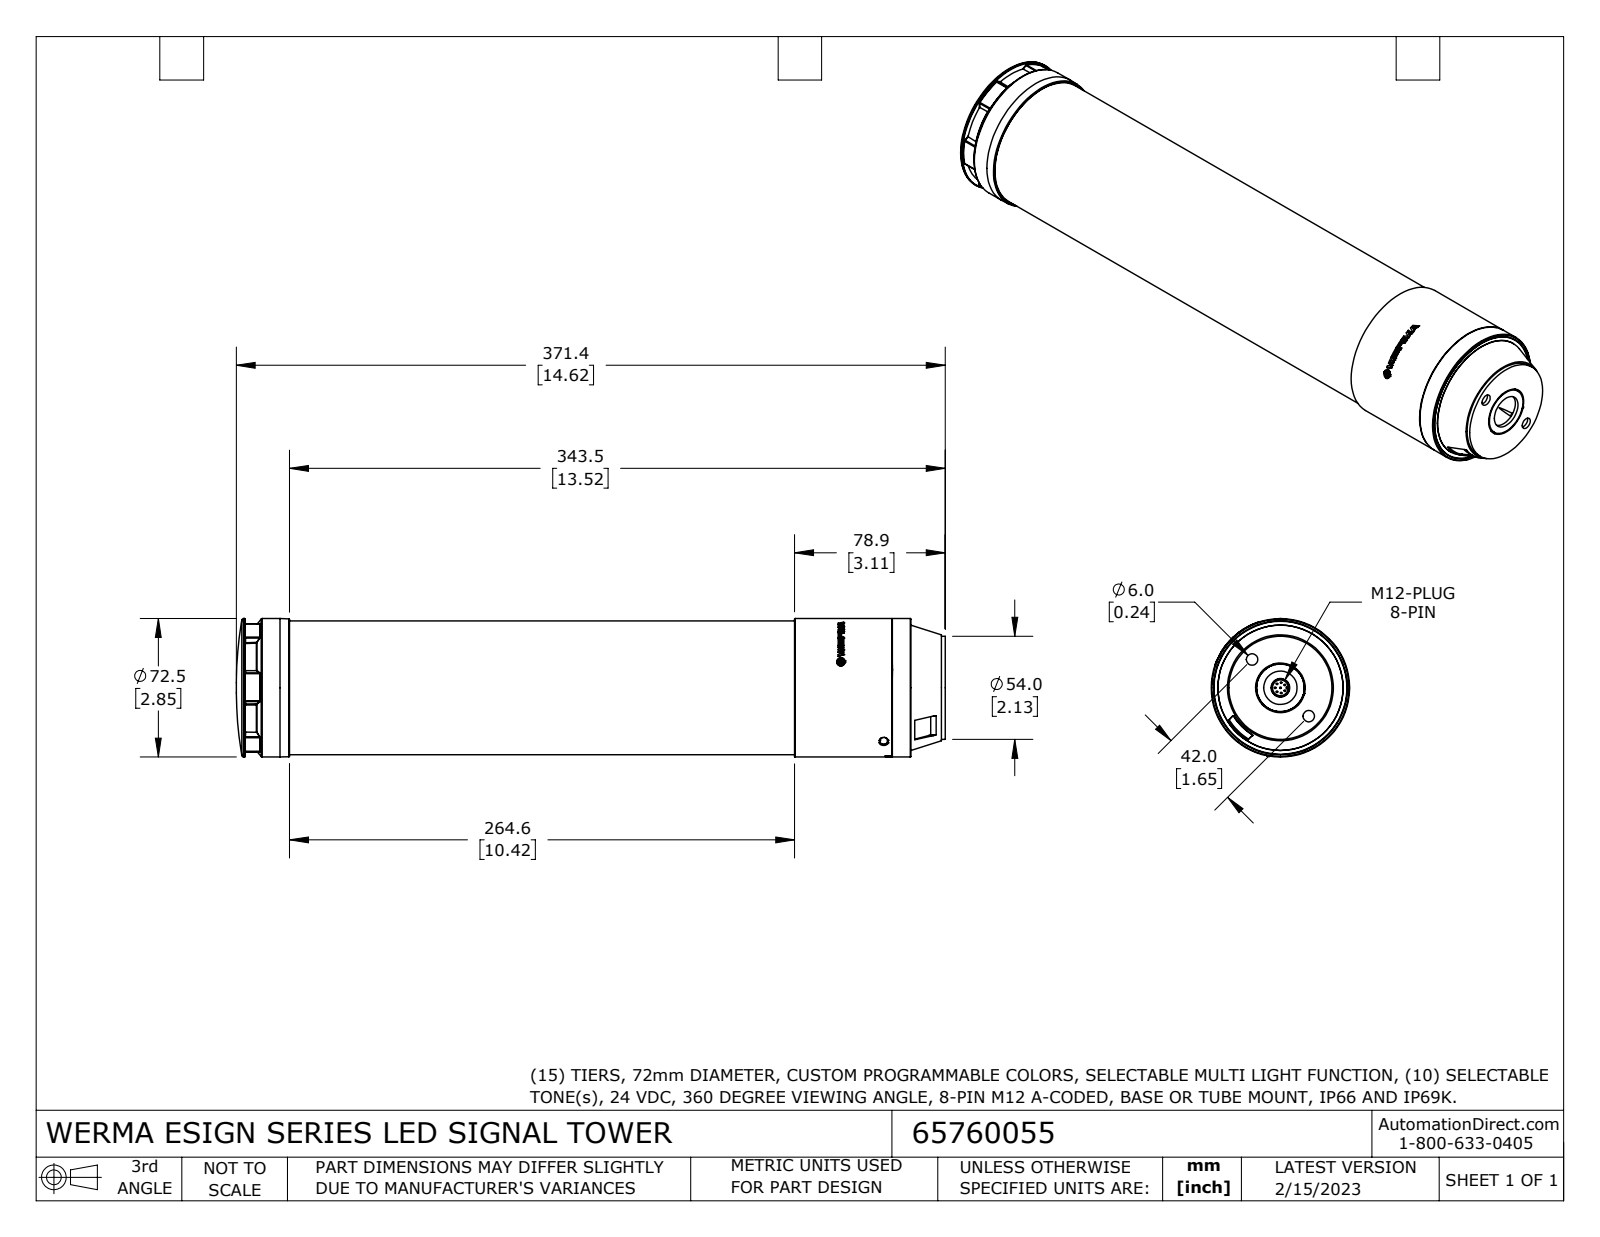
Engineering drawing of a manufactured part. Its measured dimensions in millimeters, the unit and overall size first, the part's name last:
Units: millimetres
Overall size (bounding box): 371.4 × 72.5 × 72.5
Round holes (diameter × count): ⌀6 ×2, ⌀8.3 ×1, ⌀9.7 ×1, ⌀17.5 ×1, ⌀26 ×1
Round bosses / shafts (diameter × count): ⌀0.8 ×8, ⌀72.5 ×1, ⌀70 ×1, ⌀54 ×1, ⌀24.9 ×1, ⌀4.4 ×1
Partial cylindrical surfaces — rounded edges, fillets, slot ends (radius × count): R0.3 ×12, R0.7 ×12, R2 ×2, R2 ×2, R2.5 ×2, R0.2 ×1, R0.3 ×1, R0.4 ×1
Main face-to-face distances: 360.9, 2, 358.9, 24.9, 22.9, 336, 18.1, 16.1, 6.8, 342.7
Hole centre spacings: 21, 42
Volume: 1 388 000 mm³ · Surface area: 100 600 mm²
Bodies: 1 solid, 409 faces (133 planar, 126 cylindrical, 150 other)
Part name (STEP PRODUCT): 65760055
STEP written by: SolidWorks 2021 (CONFIG_CONTROL_DESIGN)
